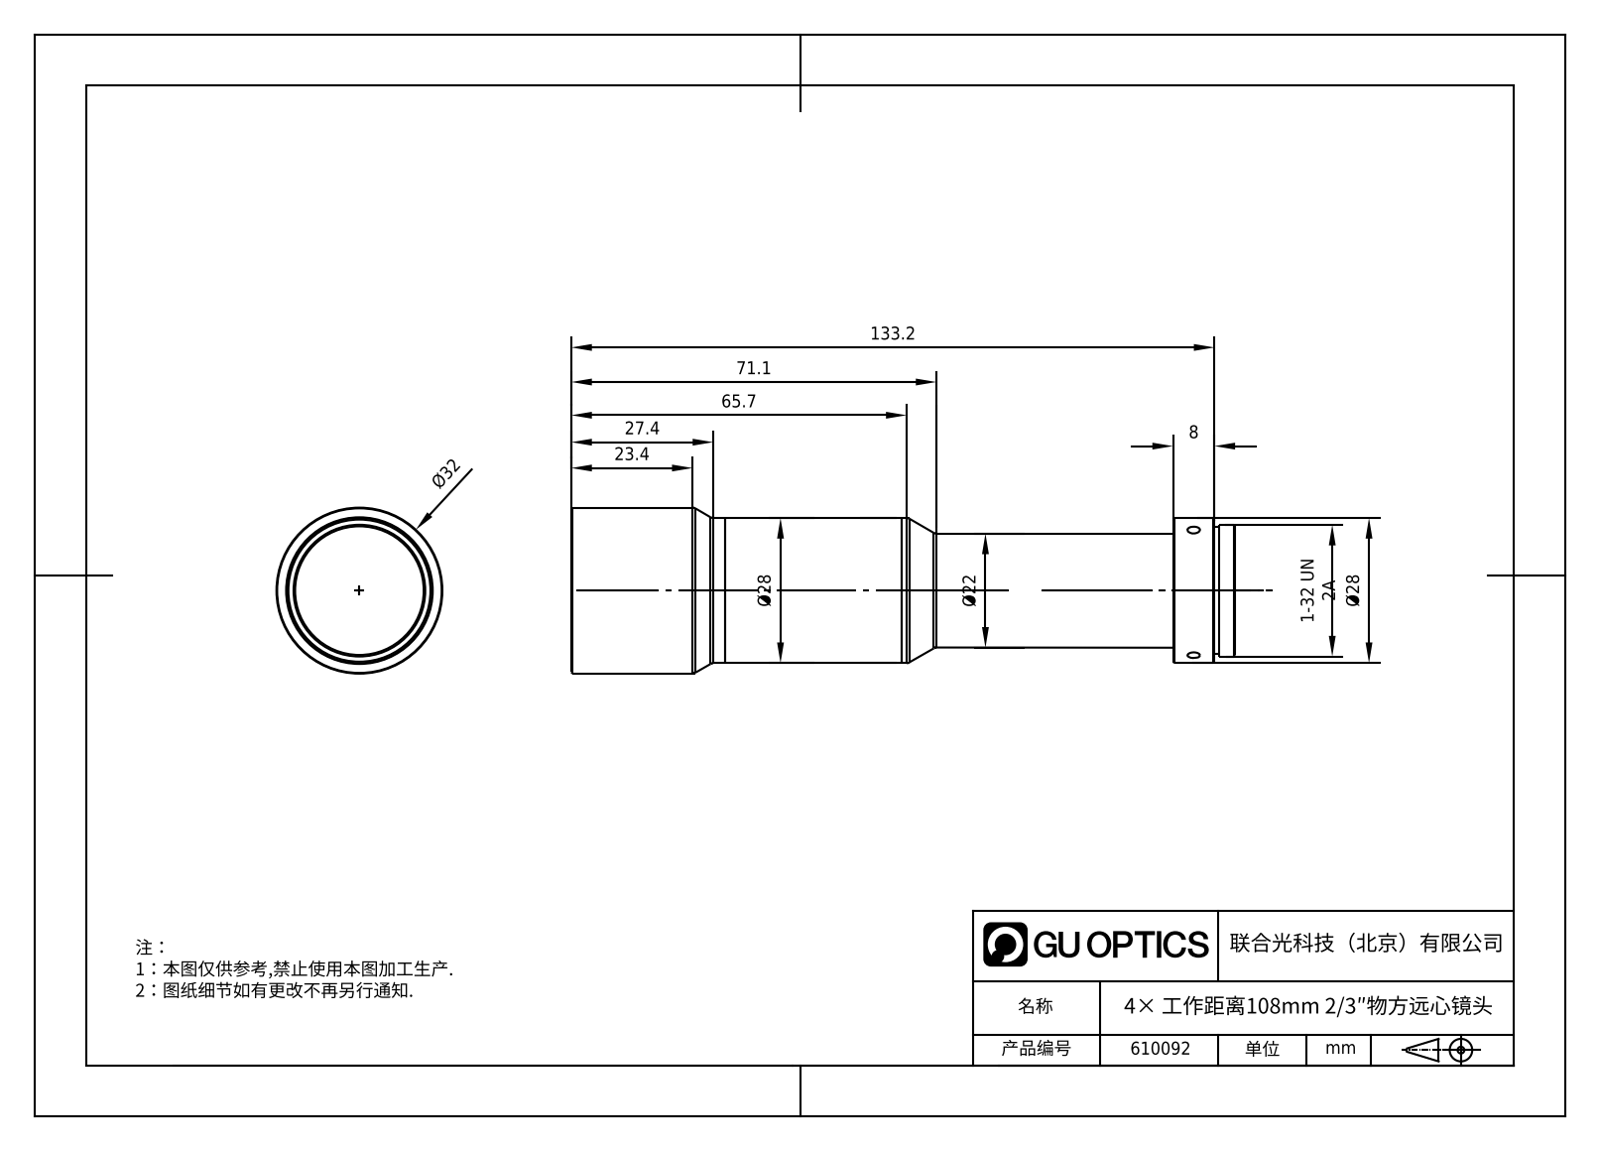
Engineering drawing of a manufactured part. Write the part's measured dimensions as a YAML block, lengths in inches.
part_name: "WWH40-108ATV2"
step_written_by: "SolidWorks 2017 (CONFIG_CONTROL_DESIGN)"
units: inches
bodies: {solids: 1, faces: 40, planar: 6, cylindrical: 14, other: 20}
overall_size: [5.402, 1.26, 1.26]
volume: 4.493
surface_area: 20.6
round_holes:
  - {diameter: 1.181, count: 1}
round_bosses_or_shafts:
  - {diameter: 1.26, count: 1}
  - {diameter: 1.102, count: 1}
  - {diameter: 1, count: 1}
  - {diameter: 0.961, count: 1}
  - {diameter: 0.866, count: 1}
face_to_face_distances: [5.303, 4.831, 0.472, 5.146, 0.315, 0.157, 0.098, 4.929, 5.244, 5.402]
